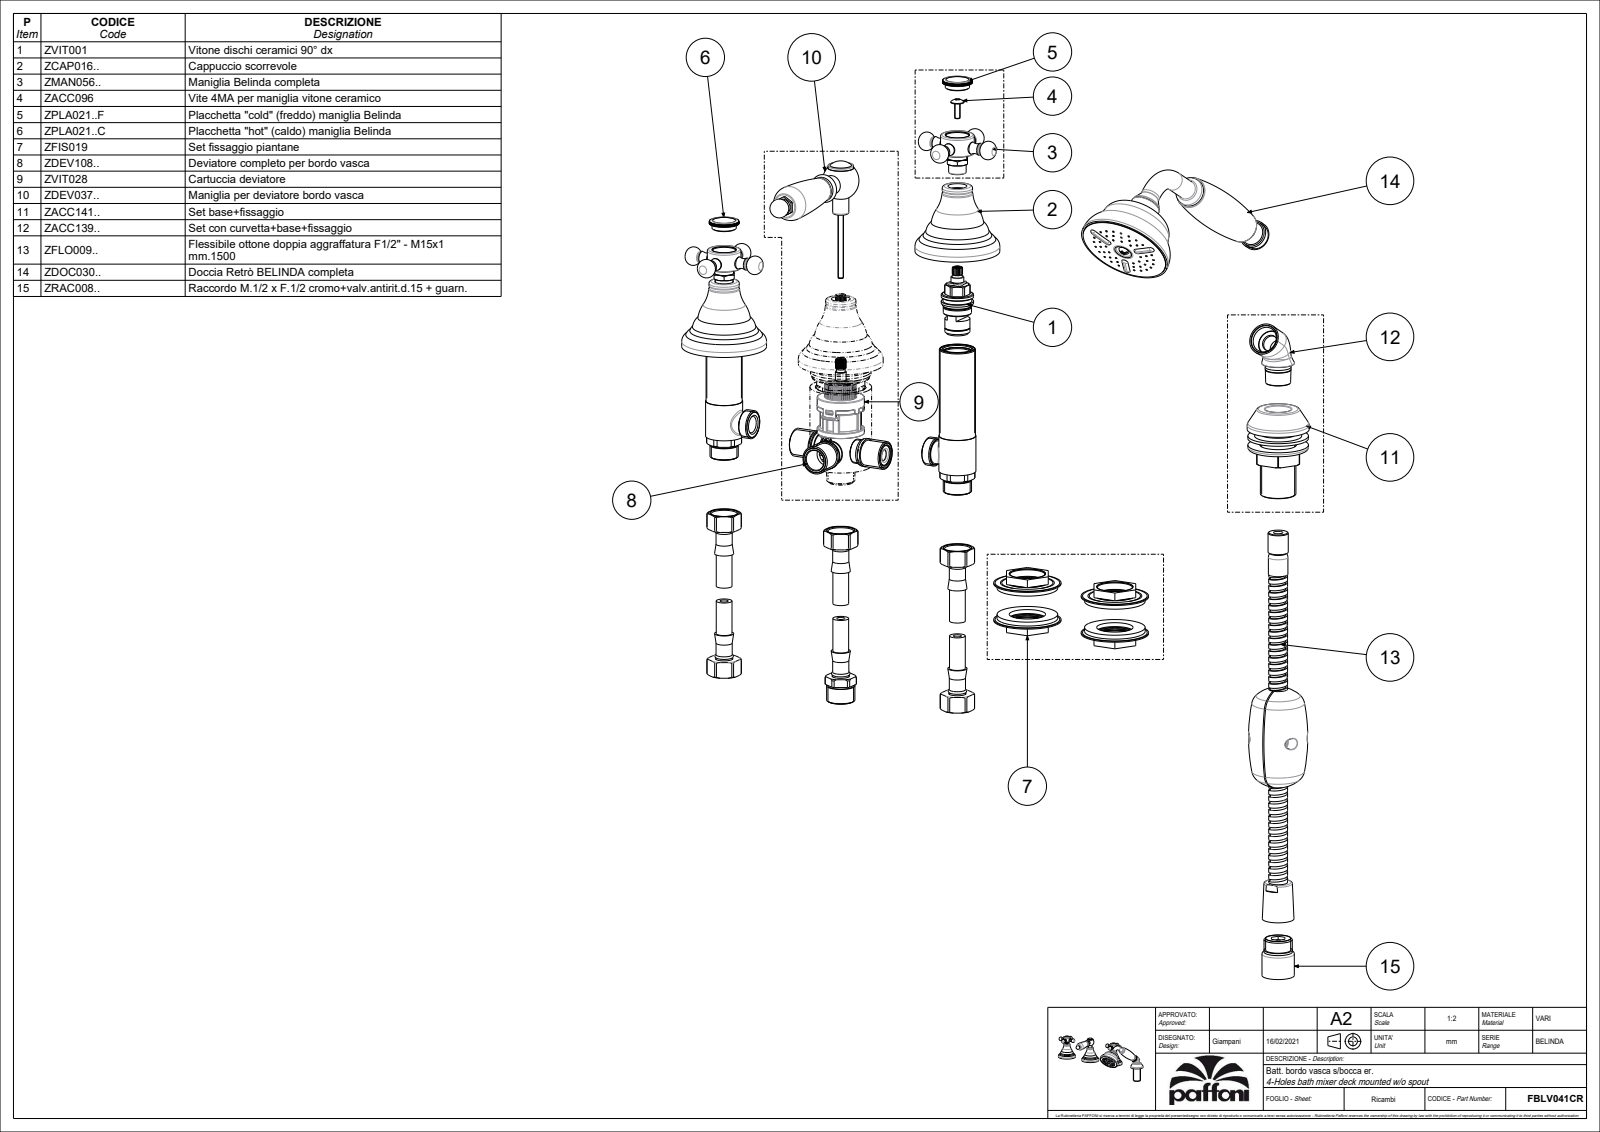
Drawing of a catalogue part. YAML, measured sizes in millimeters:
part_name: "FBLV041CR"
step_written_by: "CREO PARAMETRIC BY PTC INC, 2020044 (CONFIG_CONTROL_DESIGN)"
units: millimeters
bodies: {solids: 4, faces: 1240, planar: 470, cylindrical: 396, other: 374}
overall_size: [366.54, 262.94, 116.4]
volume: 472792
surface_area: 86932
round_holes:
  - {diameter: 1.2, count: 45}
round_bosses_or_shafts:
  - {diameter: 14, count: 5}
  - {diameter: 63, count: 3}
  - {diameter: 22.5, count: 3}
  - {diameter: 9, count: 3}
  - {diameter: 7, count: 3}
  - {diameter: 25, count: 2}
  - {diameter: 13, count: 2}
  - {diameter: 69, count: 1}
partial_cylinders:
  - {radius: 11, count: 2}
face_to_face_distances: [60.4, 50, 10.4, 15.7, 34.3, 44.7, 31.01, 15, 14, 15.2]
hole_center_spacings: [12.42, 13.78, 17.23, 20.88, 18.37, 33.28, 37.69, 6.26]
